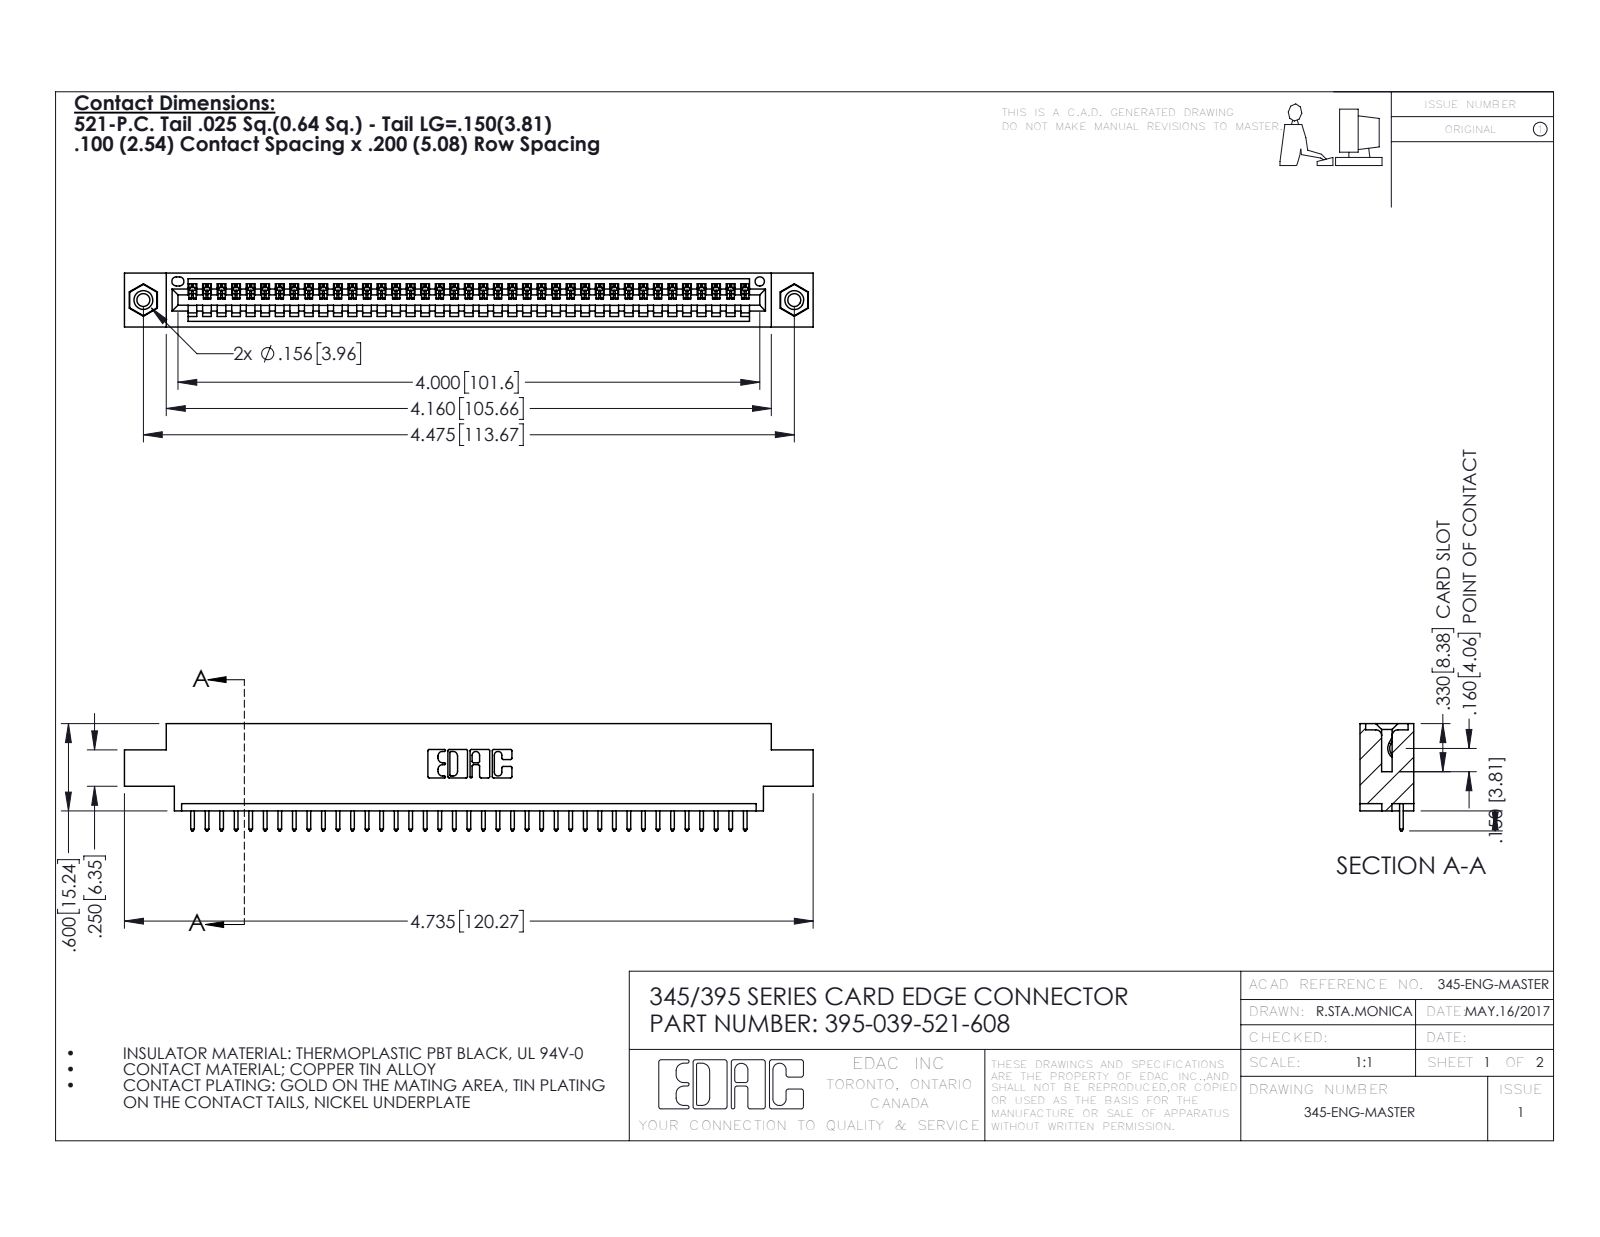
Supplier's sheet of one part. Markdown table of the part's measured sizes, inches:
| quantity | value |
| --- | --- |
| part name | 345 Part_0.170 Offset - 0.156 Dia-TI; 395-039-521-608; 345-250-001_345-250-003-102; 345-292-001_345-293-121 |
| STEP written by | SolidWorks 2016 (CONFIG_CONTROL_DESIGN) |
| units | inches |
| bodies | 42 solids, 2452 faces (1676 planar, 760 cylindrical, 16 other) |
| overall size | 4.735 × 0.737 × 0.37 |
| volume | 0.682 in³ |
| surface area | 22.49 in² |
| round holes (diameter × count) | 0.089 × 2, 0.125 × 2, 0.156 × 2, 0.064 × 1 |
| round bosses / shafts (diameter × count) | 0.155 × 2 |
| partial cylindrical surfaces (radius × count) | 0.006 × 78, 0.01 × 78, 0.01 × 22, 0.007 × 6, 0.031 × 6, 0.026 × 3, 0.031 × 2, 0.04 × 2 |
| main face-to-face distances | 0.072, 0.298, 0.37, 0.2, 0.098, 0.272, 0.025, 0.225, 0.175, 0.149 |
| hole center spacings | 0.27, 4.239, 4.475 |
